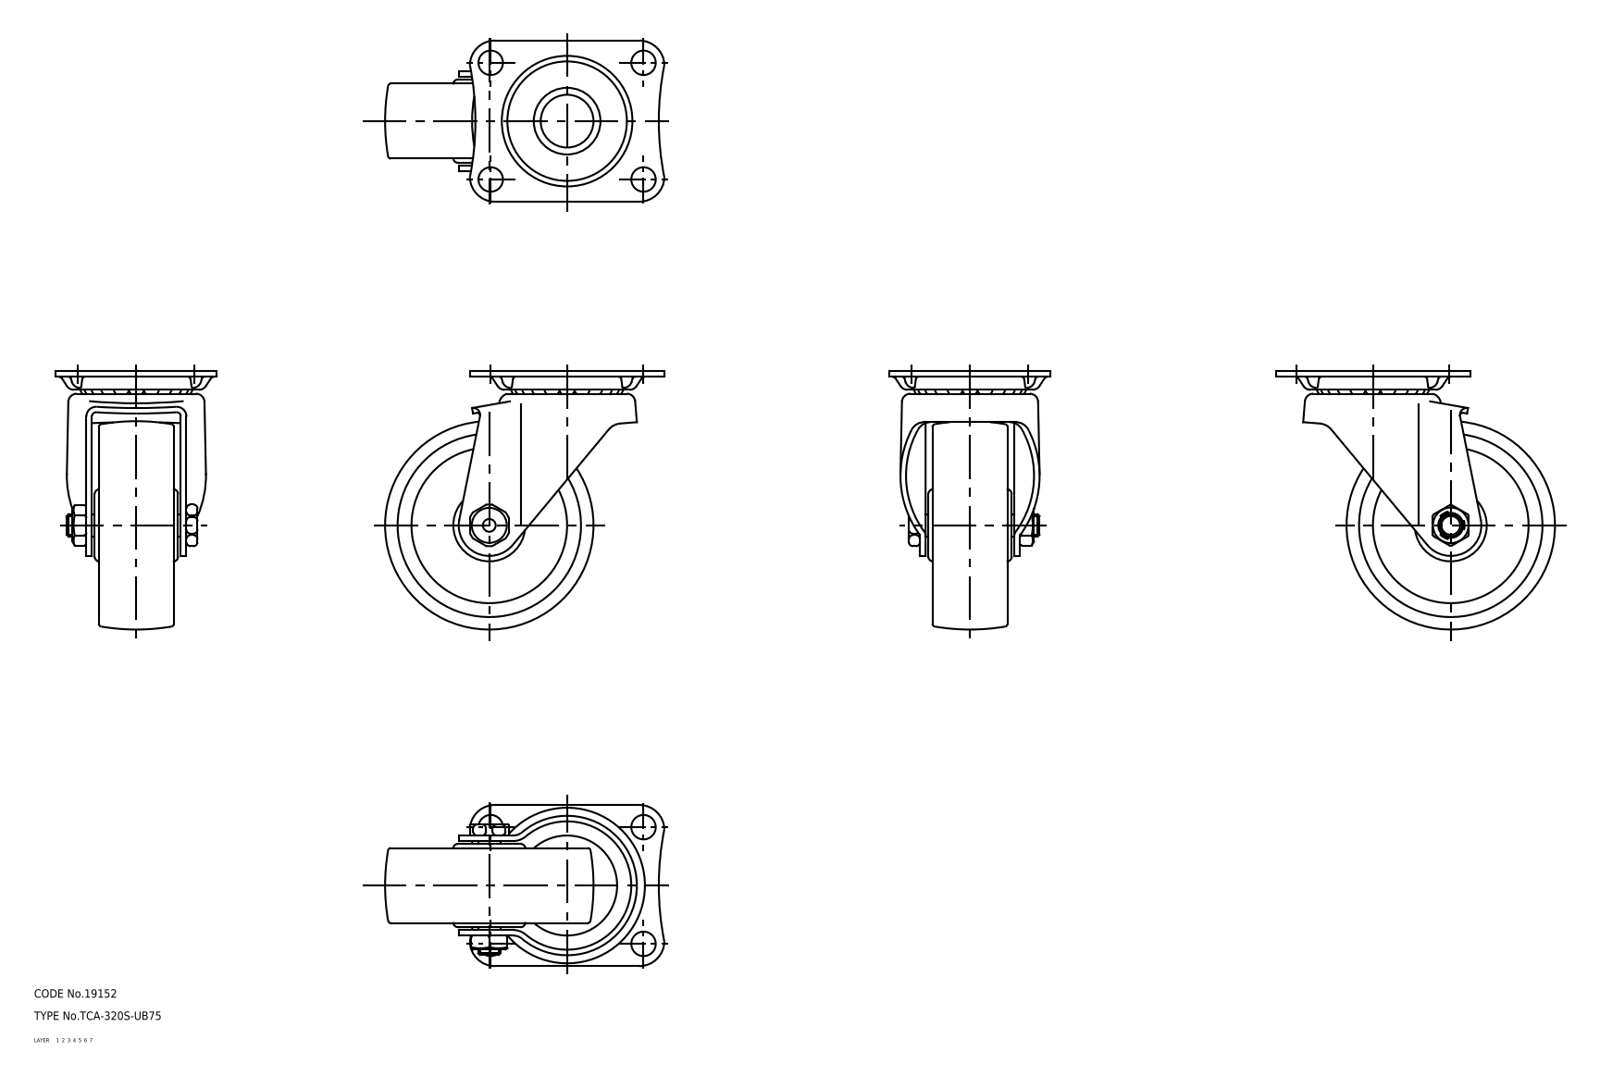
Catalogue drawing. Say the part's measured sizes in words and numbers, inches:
The part is named "wheel; mounting plate; main shaft; axle (+1 more)". Its 3-D file was written by "CADfix (AUTOMOTIVE_DESIGN)". It is 5 solids with 347 faces: 0 planar, 0 cylindrical and 347 other. Overall it measures 3.957 by 3.661 by 2.283 inches. Its volume is 8.066 cubic inches and its surface area 71.5 square inches.
